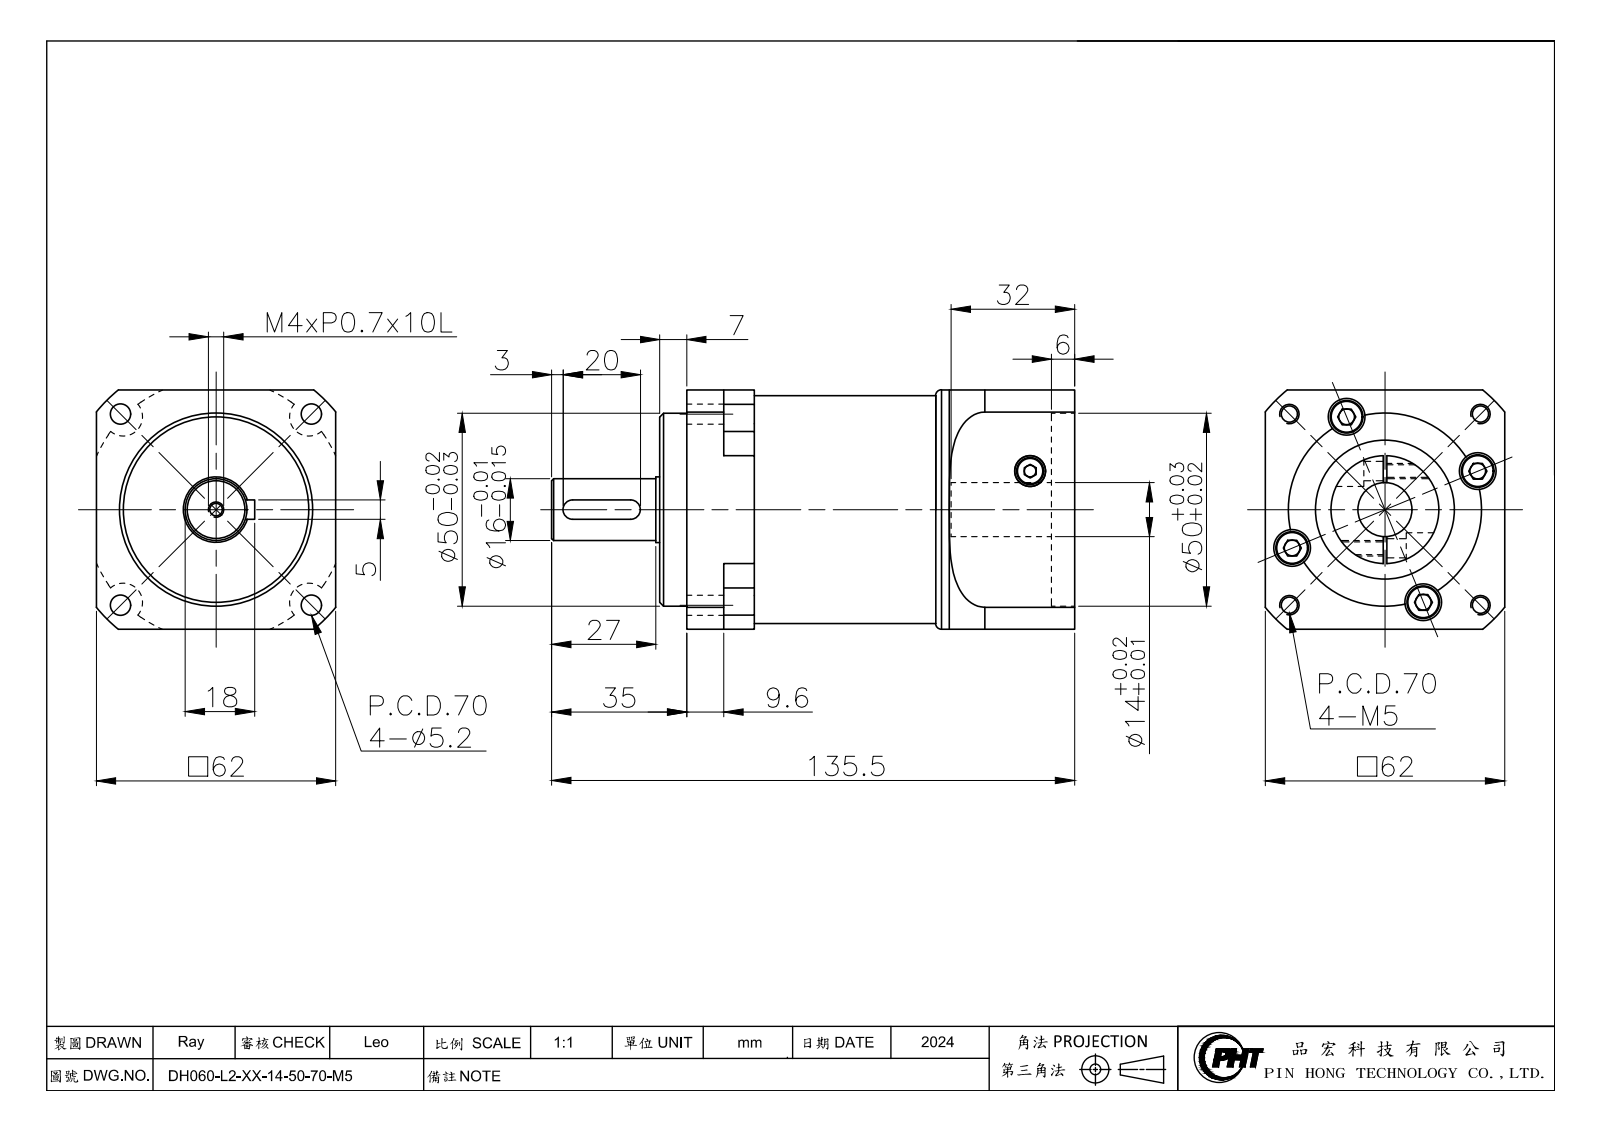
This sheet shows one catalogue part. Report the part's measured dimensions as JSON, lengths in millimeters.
{"part_name": "DH060-L2-XX-14-50-70-M5_2024", "step_written_by": "SolidWorks 2016 (CONFIG_CONTROL_DESIGN)", "units": "millimeters", "bodies": {"solids": 1, "faces": 188, "planar": 70, "cylindrical": 94, "other": 24}, "overall_size": [135.5, 62, 62], "volume_mm3": 306227, "surface_area_mm2": 46797, "round_holes": [[5.2, 8], [4.2, 4], [9.5, 4], [8, 2], [3.3, 1], [14, 1], [36, 1], [50, 1]], "round_bosses_or_shafts": [[8.5, 4], [61.8, 1], [59, 1], [28, 1], [17, 1], [16, 1]], "partial_cylinders_radius": [[5, 4], [2.5, 2], [34, 1], [40, 1]], "face_to_face_distances": [62, 7, 100.5, 107.5, 101.5, 6, 94.5, 1, 30.5, 31.5], "hole_center_spacings": [14.82, 26, 34.71, 35, 36.77, 49.5, 50.97, 59.85]}
